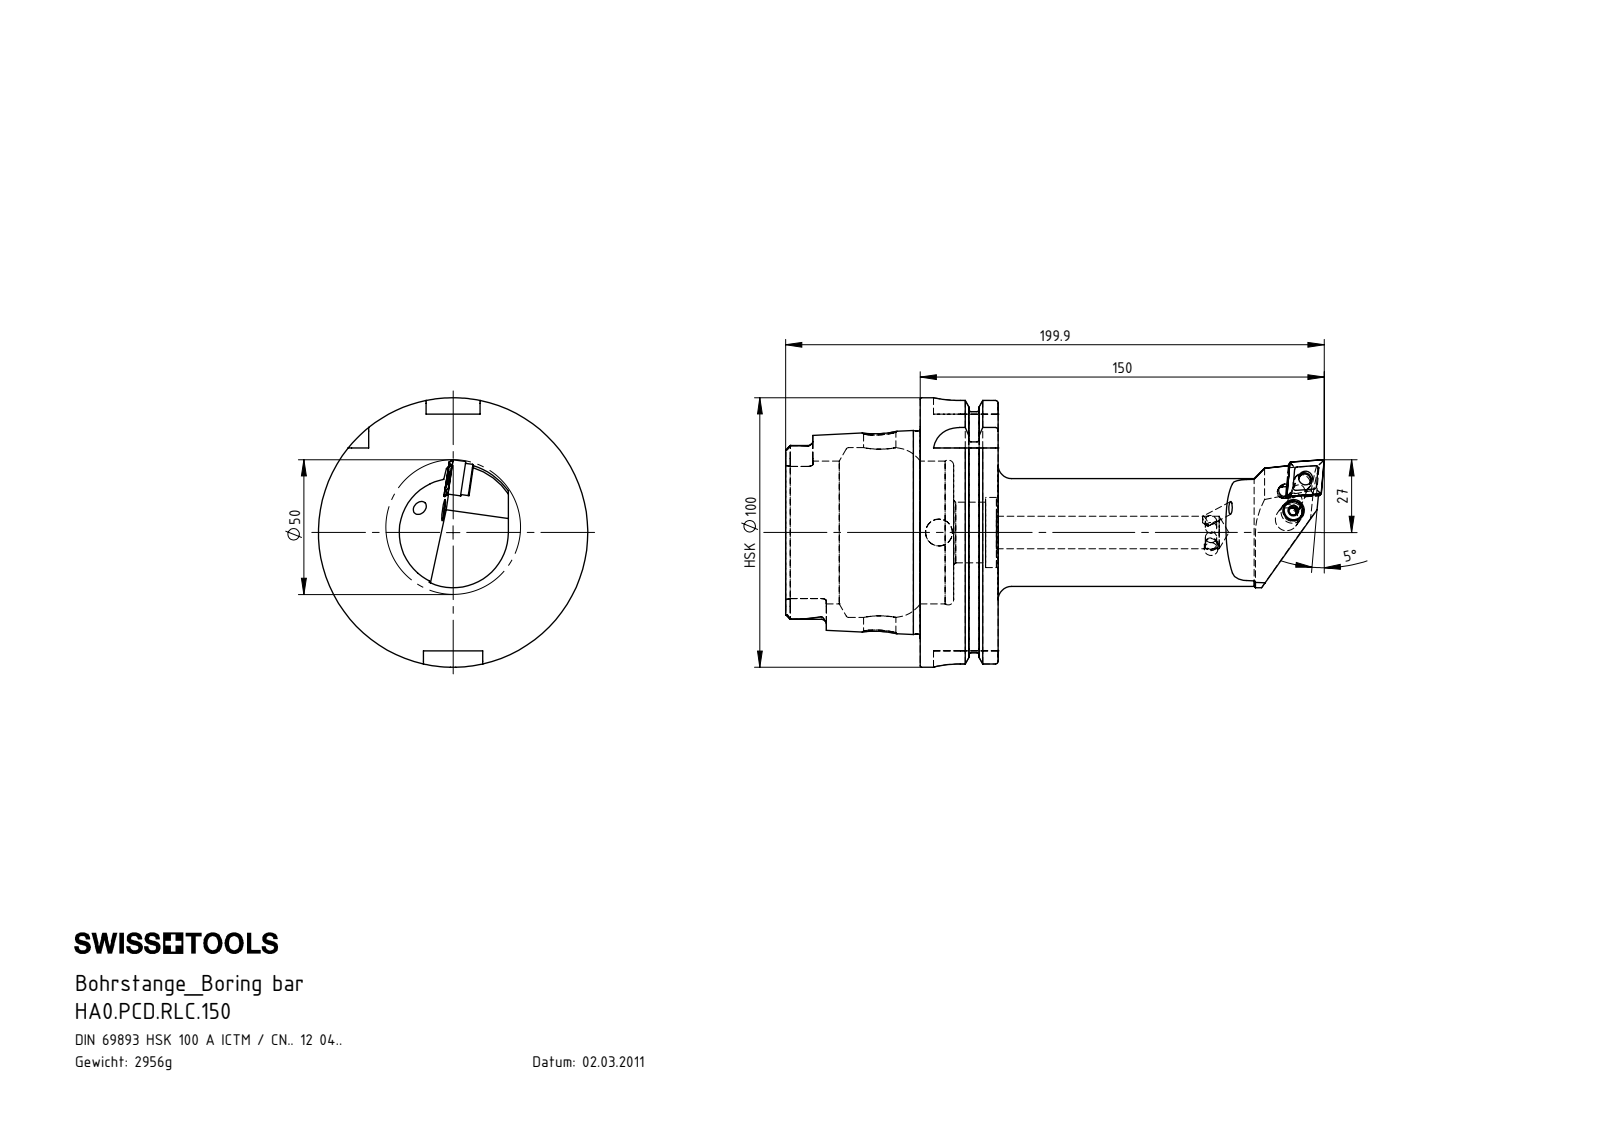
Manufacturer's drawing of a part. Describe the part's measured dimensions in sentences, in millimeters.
The part is named "HA0.PCD.RLC.150; WCD-ER3.101.000_A; WCD-ER4.101.017_A; KVT_MB_600_050 (+3 more)". Its 3-D file was written by "SolidWorks 2012 (CONFIG_CONTROL_DESIGN)". It is 7 solids with 366 faces: 111 planar, 104 cylindrical and 151 other. Overall it measures 199.9 by 100 by 100 millimeters. Its volume is 376 065 cubic millimeters and its surface area 69 764 square millimeters. Round holes: 2 of diameter 4.2, 2 of diameter 12, 1 of diameter 4, 1 of diameter 5.16, 1 of diameter 6.4, 1 of diameter 7, 1 of diameter 8.4, 1 of diameter 10, 1 of diameter 22.5, 1 of diameter 26, 1 of diameter 53, 1 of diameter 63. Round bosses or shafts: 1 of diameter 100, 1 of diameter 91.95, 1 of diameter 75.26, 1 of diameter 40, 1 of diameter 8, 1 of diameter 7.9, 1 of diameter 6.4, 1 of diameter 5. Partial cylindrical surfaces (rounded edges, fillets, slot ends): 6 of radius 1.9, 4 of radius 0.4, 4 of radius 1, 4 of radius 10, 2 of radius 2.5, 2 of radius 4.83, 2 of radius 4.88, 1 of radius 2.1. The main face-to-face distances are 28.95, 12.45, 16.5, 49.9, 62.35, 78.85, 87.8, 78.2, 28.3, 15.85. The hole center spacings are 12.8, 12.86.
